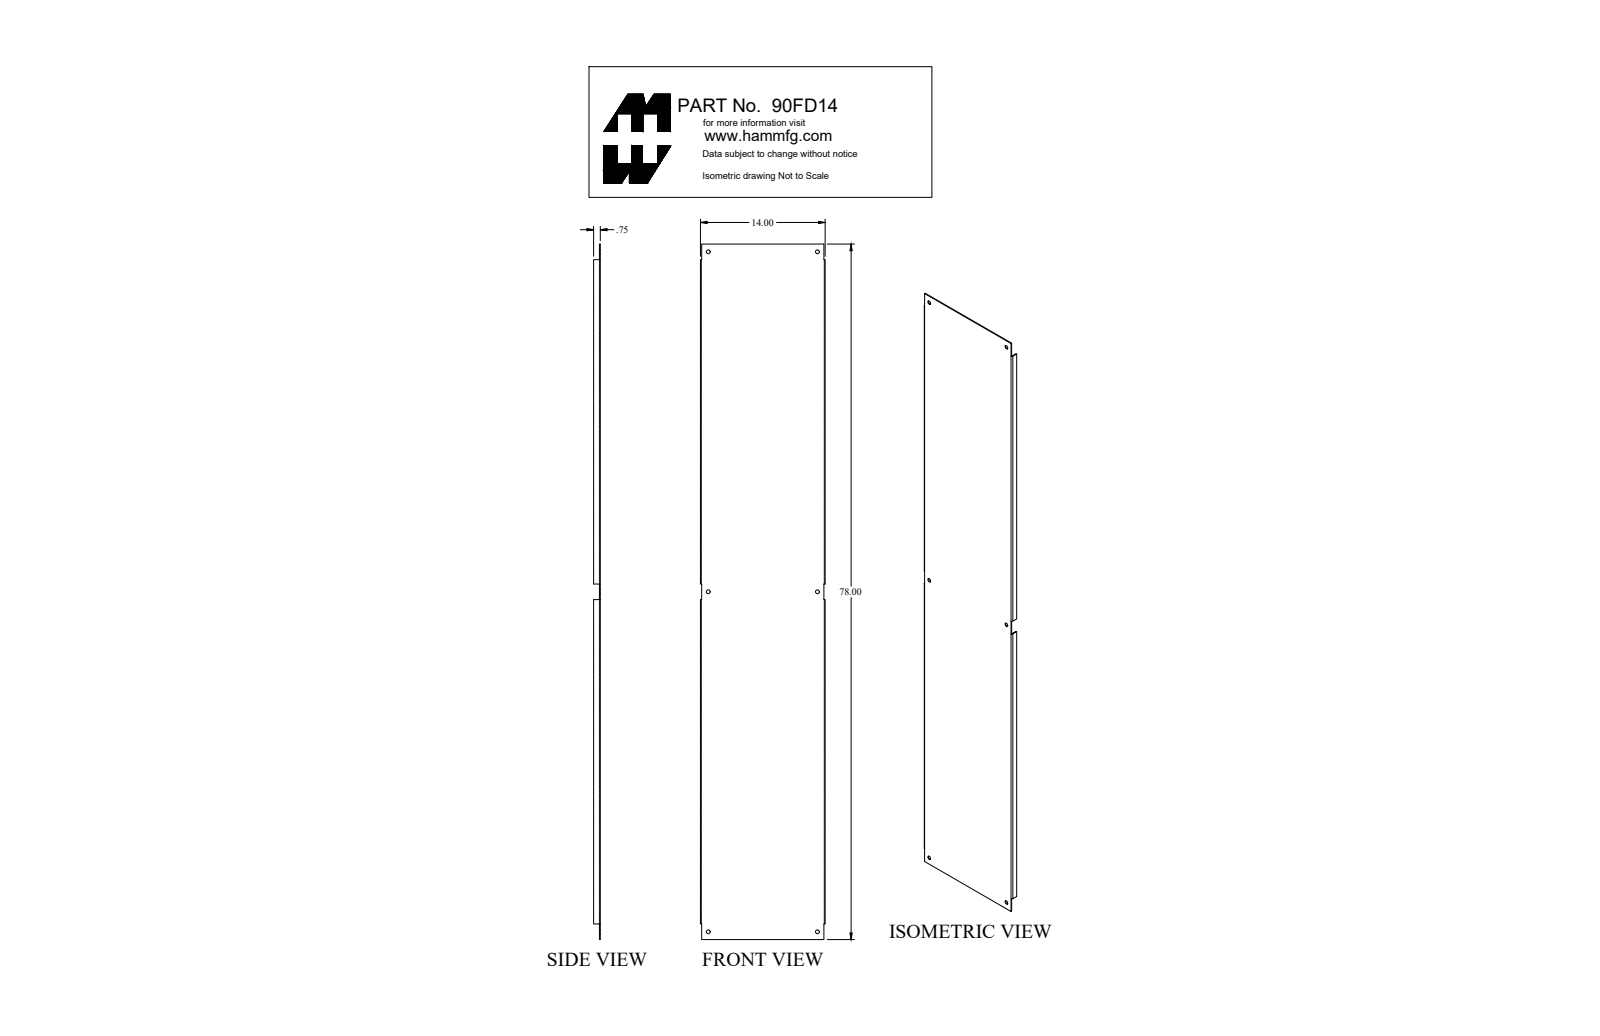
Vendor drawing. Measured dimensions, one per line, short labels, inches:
name: 90FD14_Default
written by: SolidWorks 2018 (CONFIG_CONTROL_DESIGN)
unit: in
bodies: 1 solid, 50 faces (30 planar, 20 cylindrical, 0 other)
size: 78 × 14 × 0.75
volume: 112 in³; area: 2 377 in²
holes: 6× ⌀0.437
rounds: 2× R0.048, 2× R0.143
face distances: 0.095, 13.905, 13.81, 14, 0.75, 0.655, 78, 0.143, 13.857, 0.048
hole spacings: 38.125, 40.045, 12.25, 76.25, 77.228
